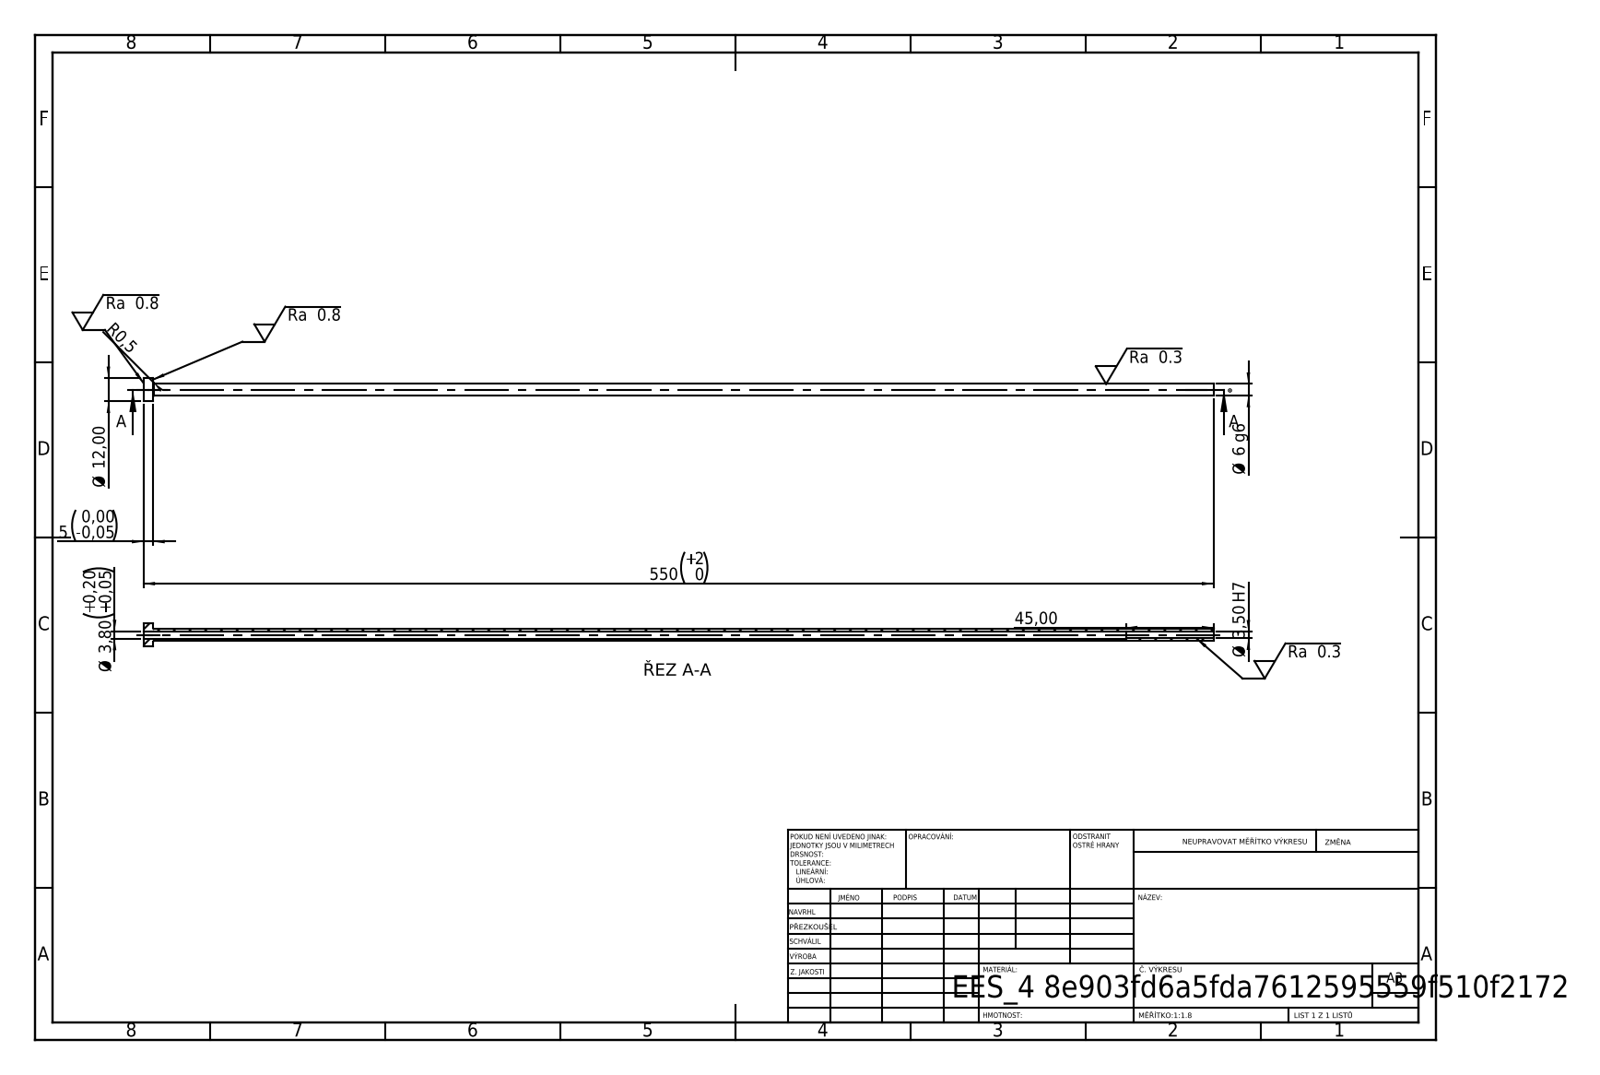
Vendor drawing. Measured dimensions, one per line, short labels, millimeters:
written by: SolidWorks 2019 (CONFIG_CONTROL_DESIGN)
unit: mm
bodies: 1 solid, 14 faces (4 planar, 8 cylindrical, 2 other)
size: 550 × 12 × 12
volume: 9 816 mm³; area: 17 188 mm²
holes: 1× ⌀3.5, 1× ⌀3.8
bosses: 1× ⌀12, 1× ⌀6
face distances: 5, 550, 545, 505, 500, 45
